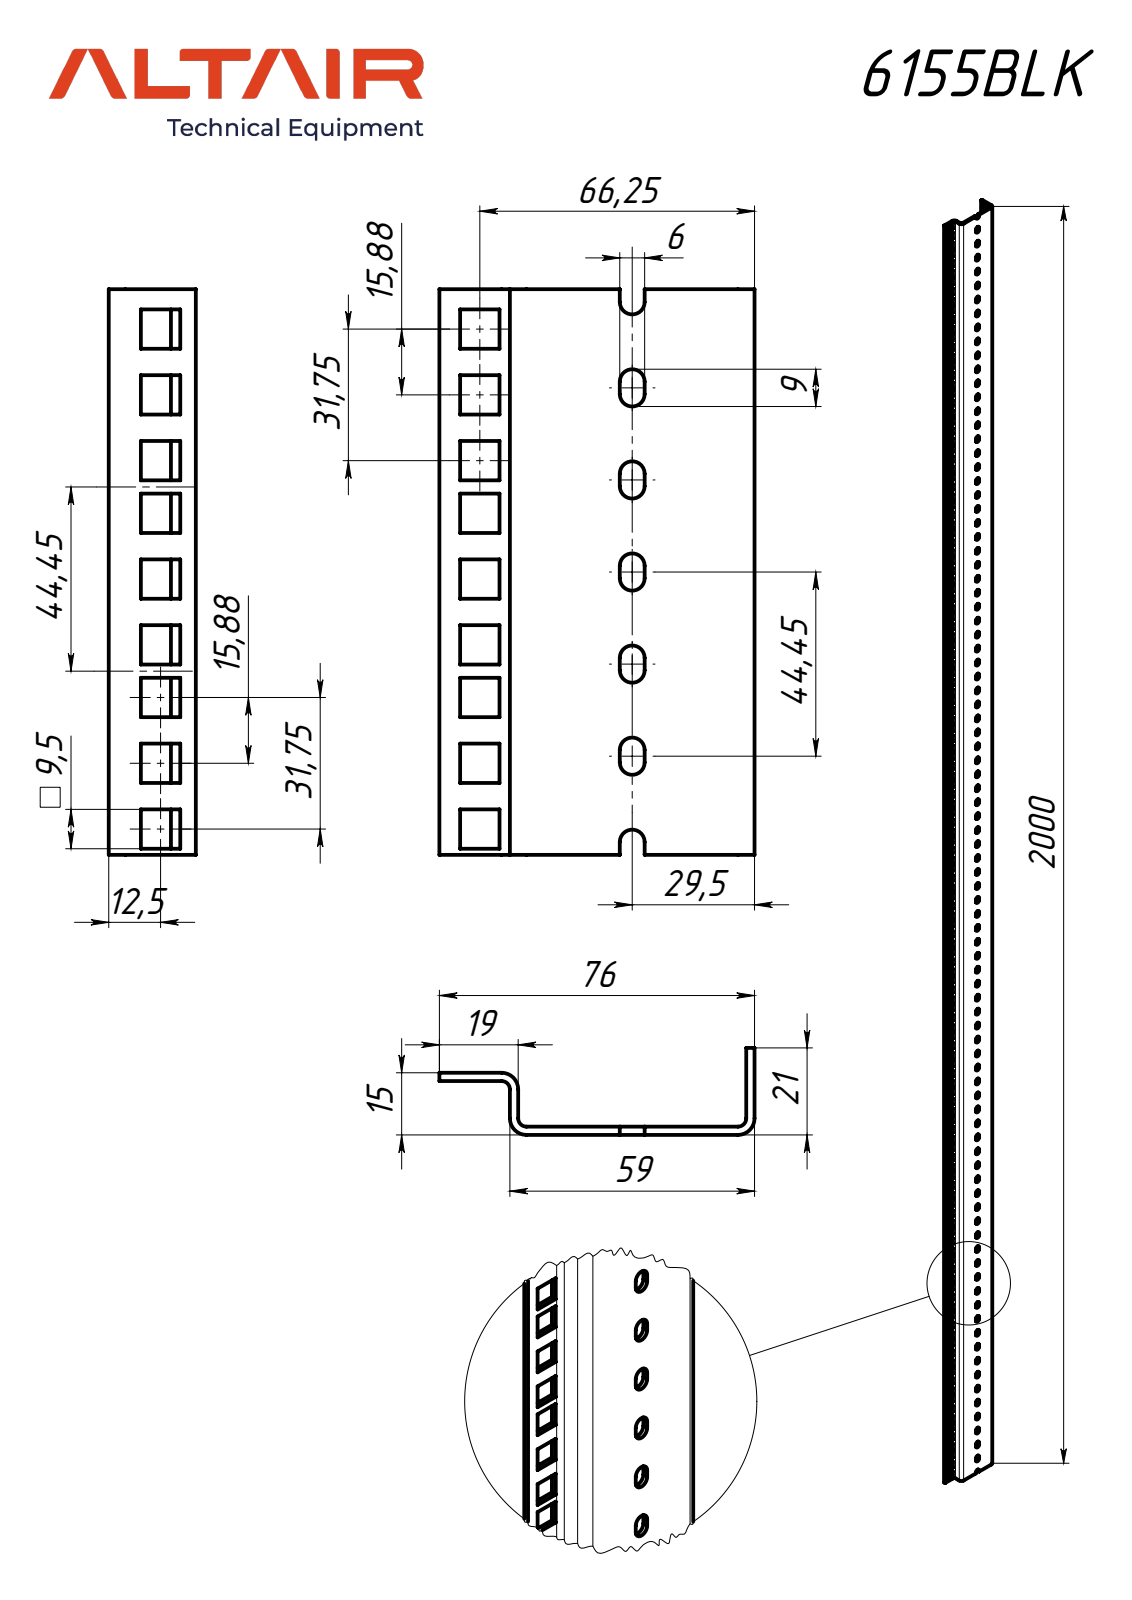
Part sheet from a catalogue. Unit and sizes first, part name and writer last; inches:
Units: inches
Overall size (bounding box): 5.374 × 2.992 × 0.827
Partial cylindrical surfaces — rounded edges, fillets, slot ends (radius × count): R0.118 ×12, R0.079 ×3, R0.157 ×3
Main face-to-face distances: 0.079, 0.512, 2.244, 0.433, 0.591, 2.323, 2.165, 0.374, 0.748, 1.75
Volume: 1.503 in³ · Surface area: 42.24 in²
Bodies: 1 solid, 120 faces (96 planar, 24 cylindrical, 0 other)
Part name (STEP PRODUCT): Rack направляющая J 6155BLK
STEP written by: SolidWorks 2018 (CONFIG_CONTROL_DESIGN)
